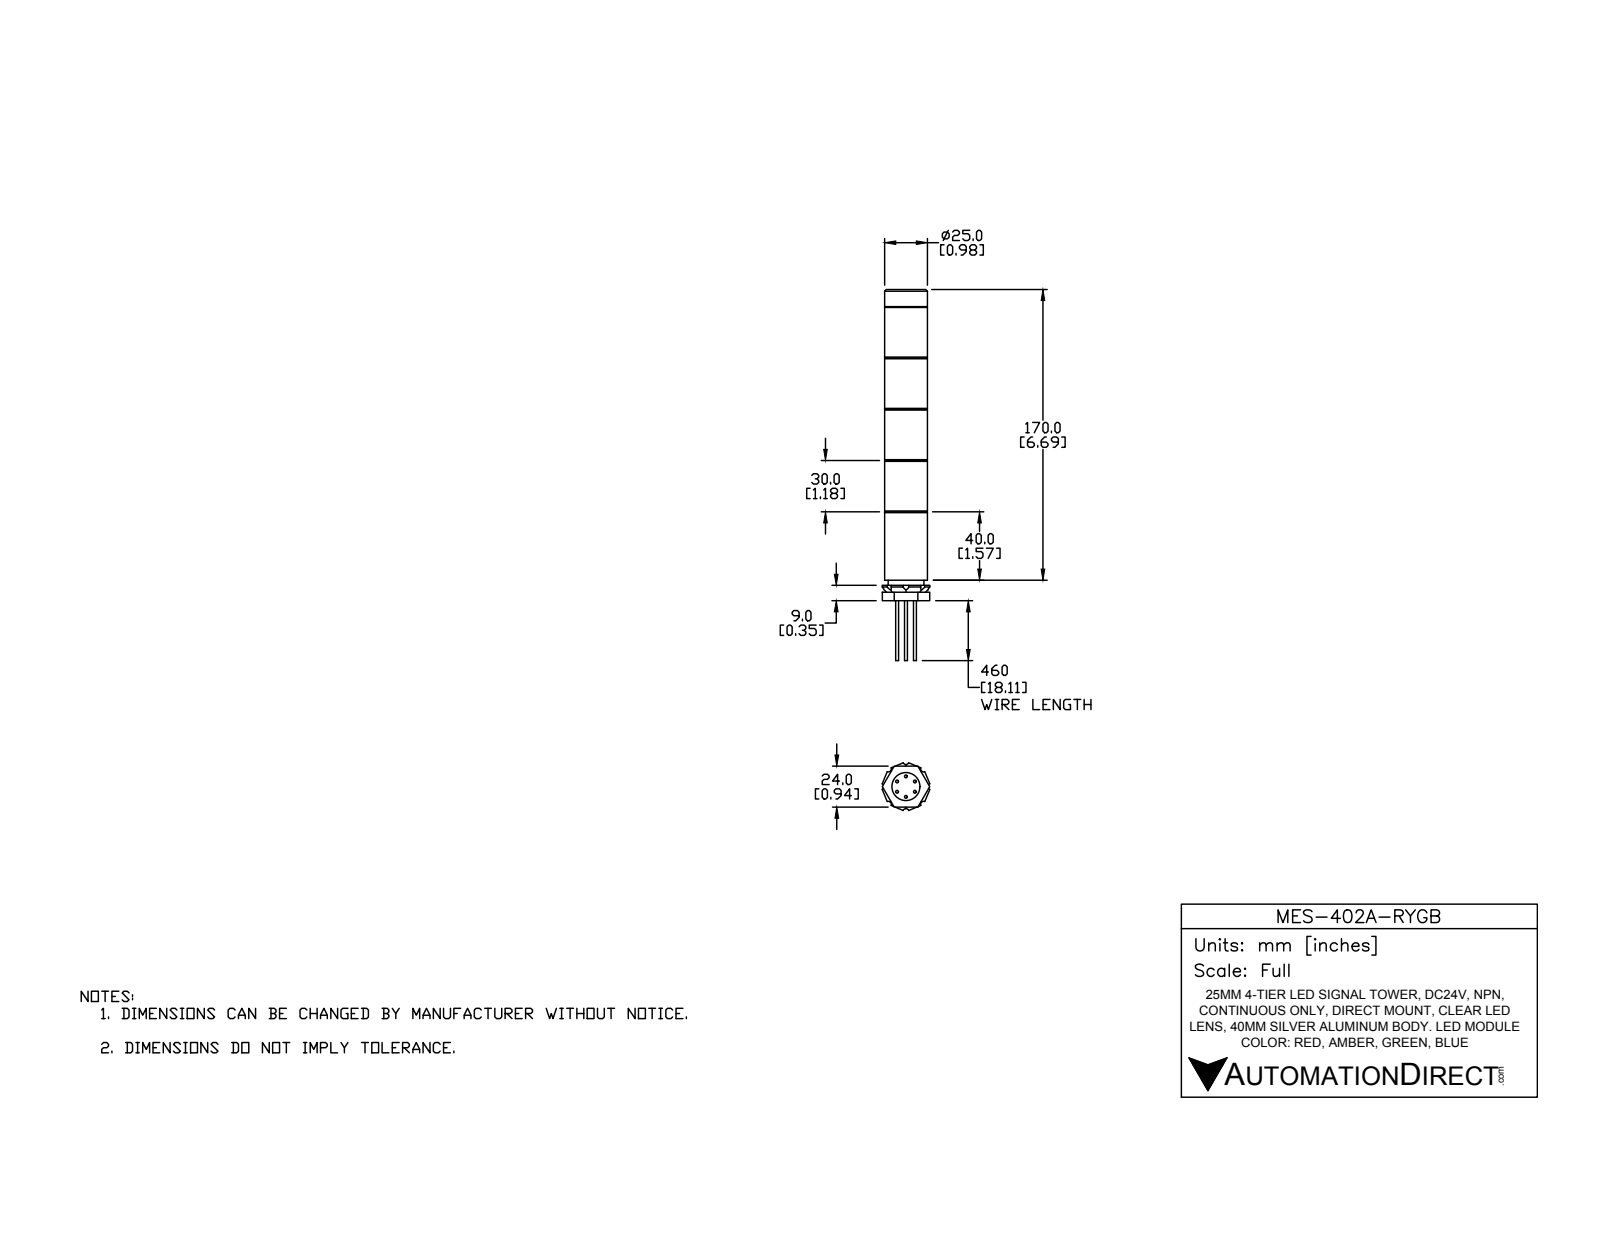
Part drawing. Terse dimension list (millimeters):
name: MES-402A-RYGB
written by: SolidWorks 2016 (AUTOMOTIVE_DESIGN)
unit: mm
bodies: 15 solids, 156 faces (77 planar, 53 cylindrical, 26 other)
size: 217 × 27.89 × 27.89
volume: 77 795 mm³; area: 28 576 mm²
holes: 1× ⌀3.2, 1× ⌀7.7, 1× ⌀16.4, 1× ⌀18, 1× ⌀20.7, 1× ⌀21
bosses: 6× ⌀1.7, 1× ⌀25, 1× ⌀20.9, 1× ⌀16, 1× ⌀5
rounds: 8× R1.75
face distances: 30, 60, 90, 120, 40, 7, 137, 70, 100, 130
